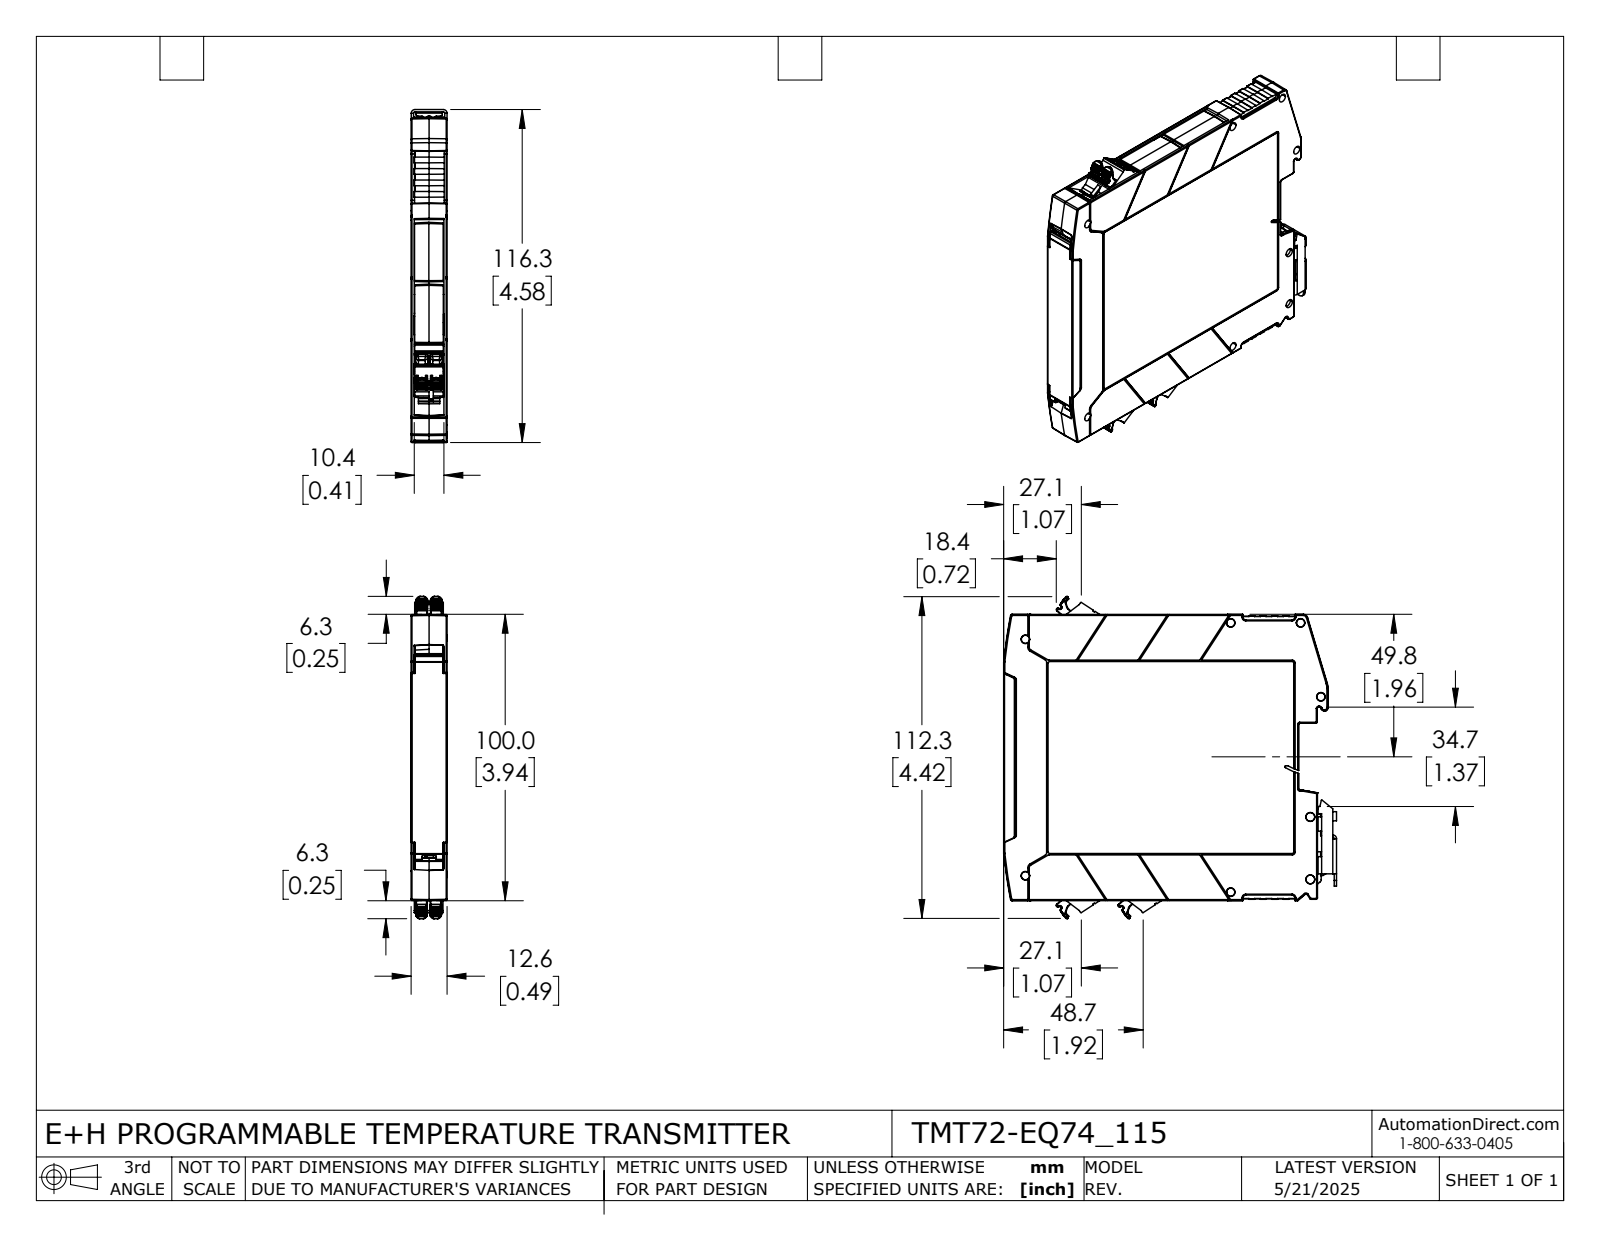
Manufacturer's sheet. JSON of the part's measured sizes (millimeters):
{"part_name": "TMT72-BQ74_115", "step_written_by": "SolidWorks 2021 (AUTOMOTIVE_DESIGN)", "units": "millimeters", "bodies": {"solids": 1, "faces": 4481, "planar": 2205, "cylindrical": 1100, "other": 1176}, "overall_size": [116.3, 112.5, 12.6], "volume_mm3": 48410, "surface_area_mm2": 63960, "round_holes": [[4.4, 1]], "round_bosses_or_shafts": [[1.4, 6], [1.5, 2], [1.3, 2]], "partial_cylinders_radius": [[0.2, 286], [0.5, 98], [0.3, 74], [1, 34], [0.8, 33], [0.2, 24], [0.1, 23], [0.4, 16]], "face_to_face_distances": [1.2, 11.3, 12.5, 10.1, 1.1, 11.5, 10.2, 0.8, 1.2, 5.2]}
